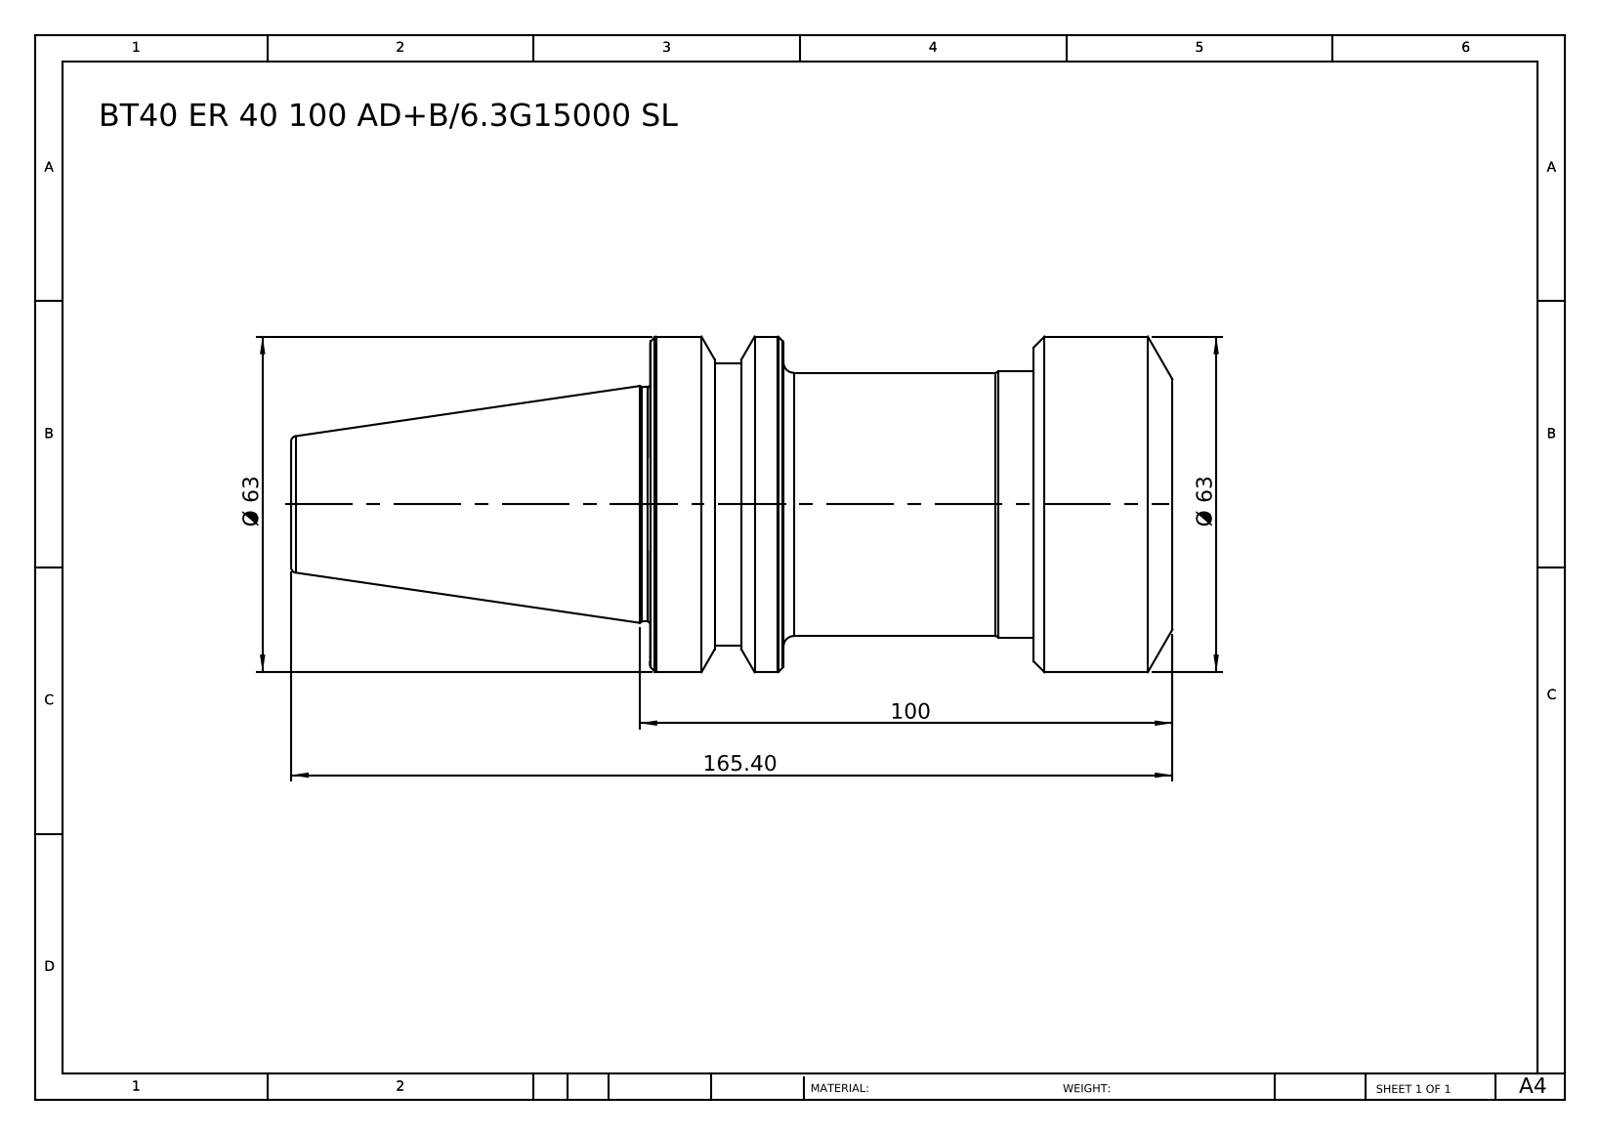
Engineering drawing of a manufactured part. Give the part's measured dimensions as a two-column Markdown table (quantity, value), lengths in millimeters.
| quantity | value |
| --- | --- |
| part name | BT40 ER 40 100 AD-6.3G15000 SL |
| STEP written by | SolidWorks 2014 (CONFIG_CONTROL_DESIGN) |
| units | millimeters |
| bodies | 1 solid, 62 faces (7 planar, 14 cylindrical, 41 other) |
| overall size | 165.4 × 63 × 63 |
| volume | 306 163 mm³ |
| surface area | 32 076 mm² |
| round bosses / shafts (diameter × count) | 63 × 1, 53 × 1, 49.9 × 1, 49.4 × 1, 44 × 1 |
| main face-to-face distances | 98, 26, 72, 73, 47, 25, 165.4, 139.4, 92.4, 67.4 |
